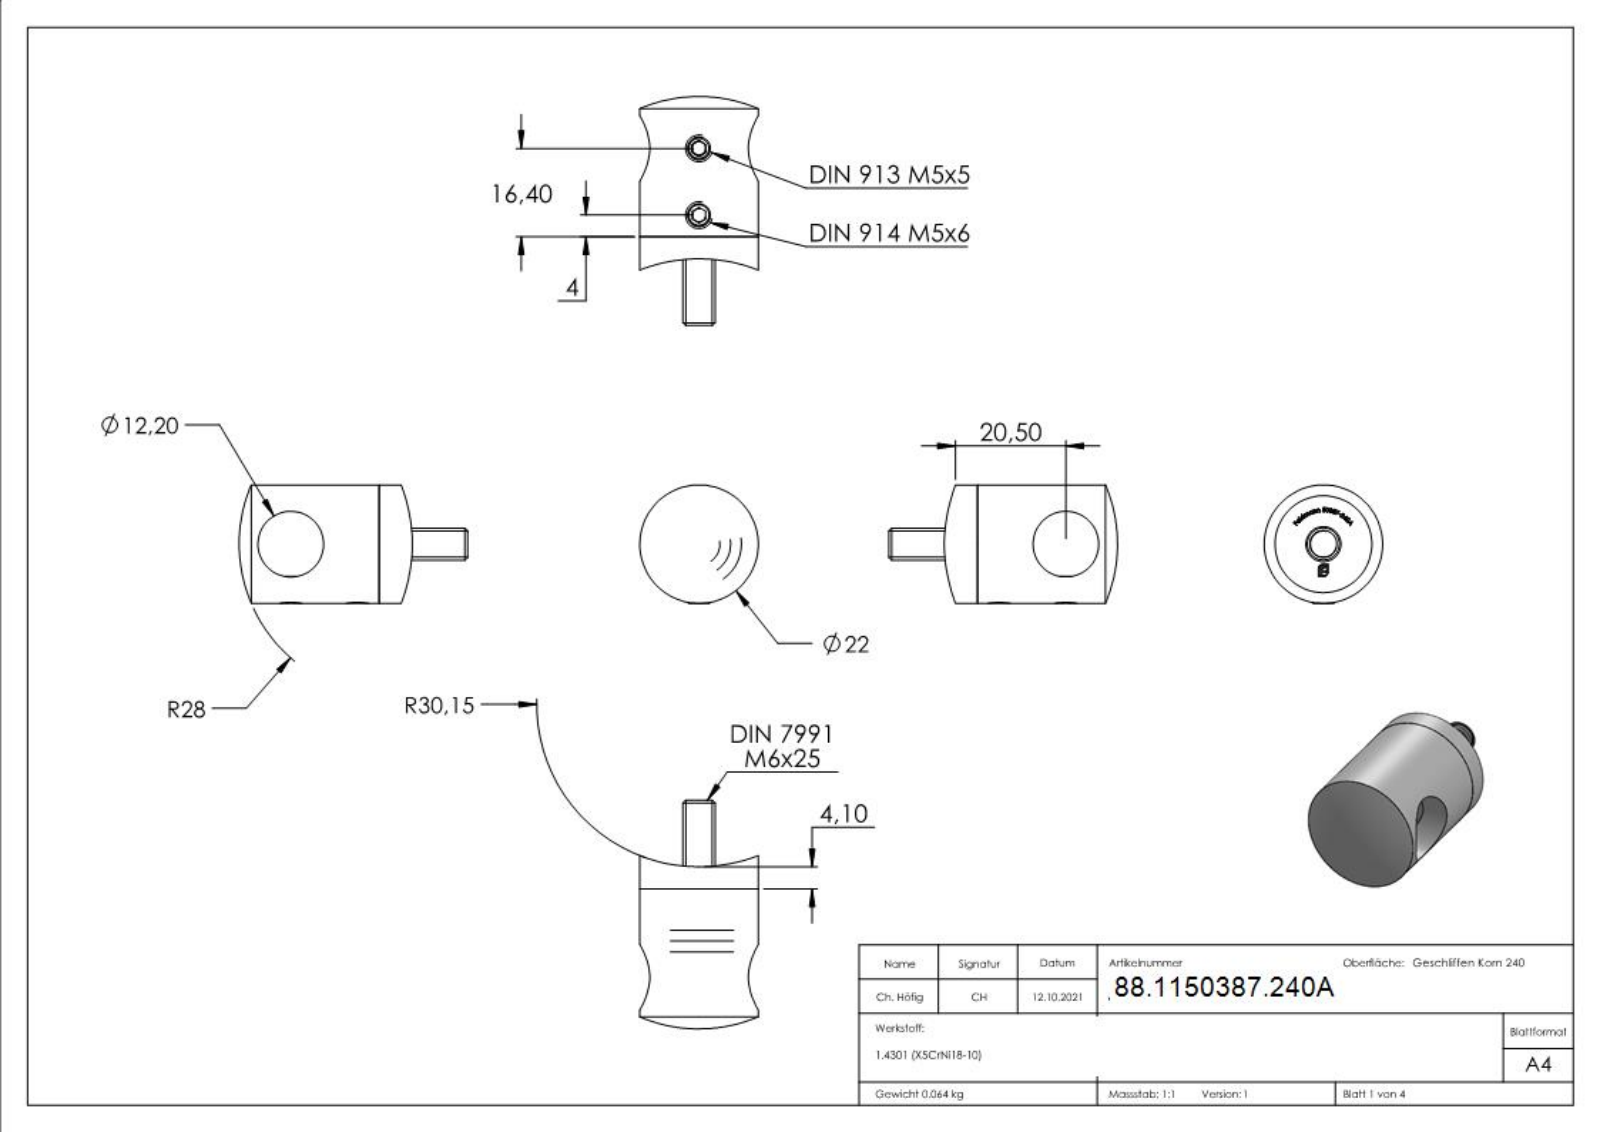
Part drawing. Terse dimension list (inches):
name: 50387-240A; Oberteil_Teil1 12,2; DIN 7991 Konfig_M6x25; DIN913 (+7 more)
written by: SolidWorks 2018 (CONFIG_CONTROL_DESIGN)
unit: in
bodies: 5 solids, 347 faces (188 planar, 15 cylindrical, 144 other)
size: 2.795 × 1.671 × 0.866
volume: 0.496 in³; area: 9.125 in²
holes: 2× ⌀0.165, 1× ⌀0.256, 1× ⌀0.472, 1× ⌀0.48, 1× ⌀0.709
bosses: 2× ⌀0.197, 1× ⌀0.866, 1× ⌀0.469, 1× ⌀0.236
rounds: 1× R1.187
face distances: 0.083, 0.419, 0.337, 0.098, 0.041, 0.378, 0.295, 0.565, 0.648, 0.943
hole spacings: 0.488
